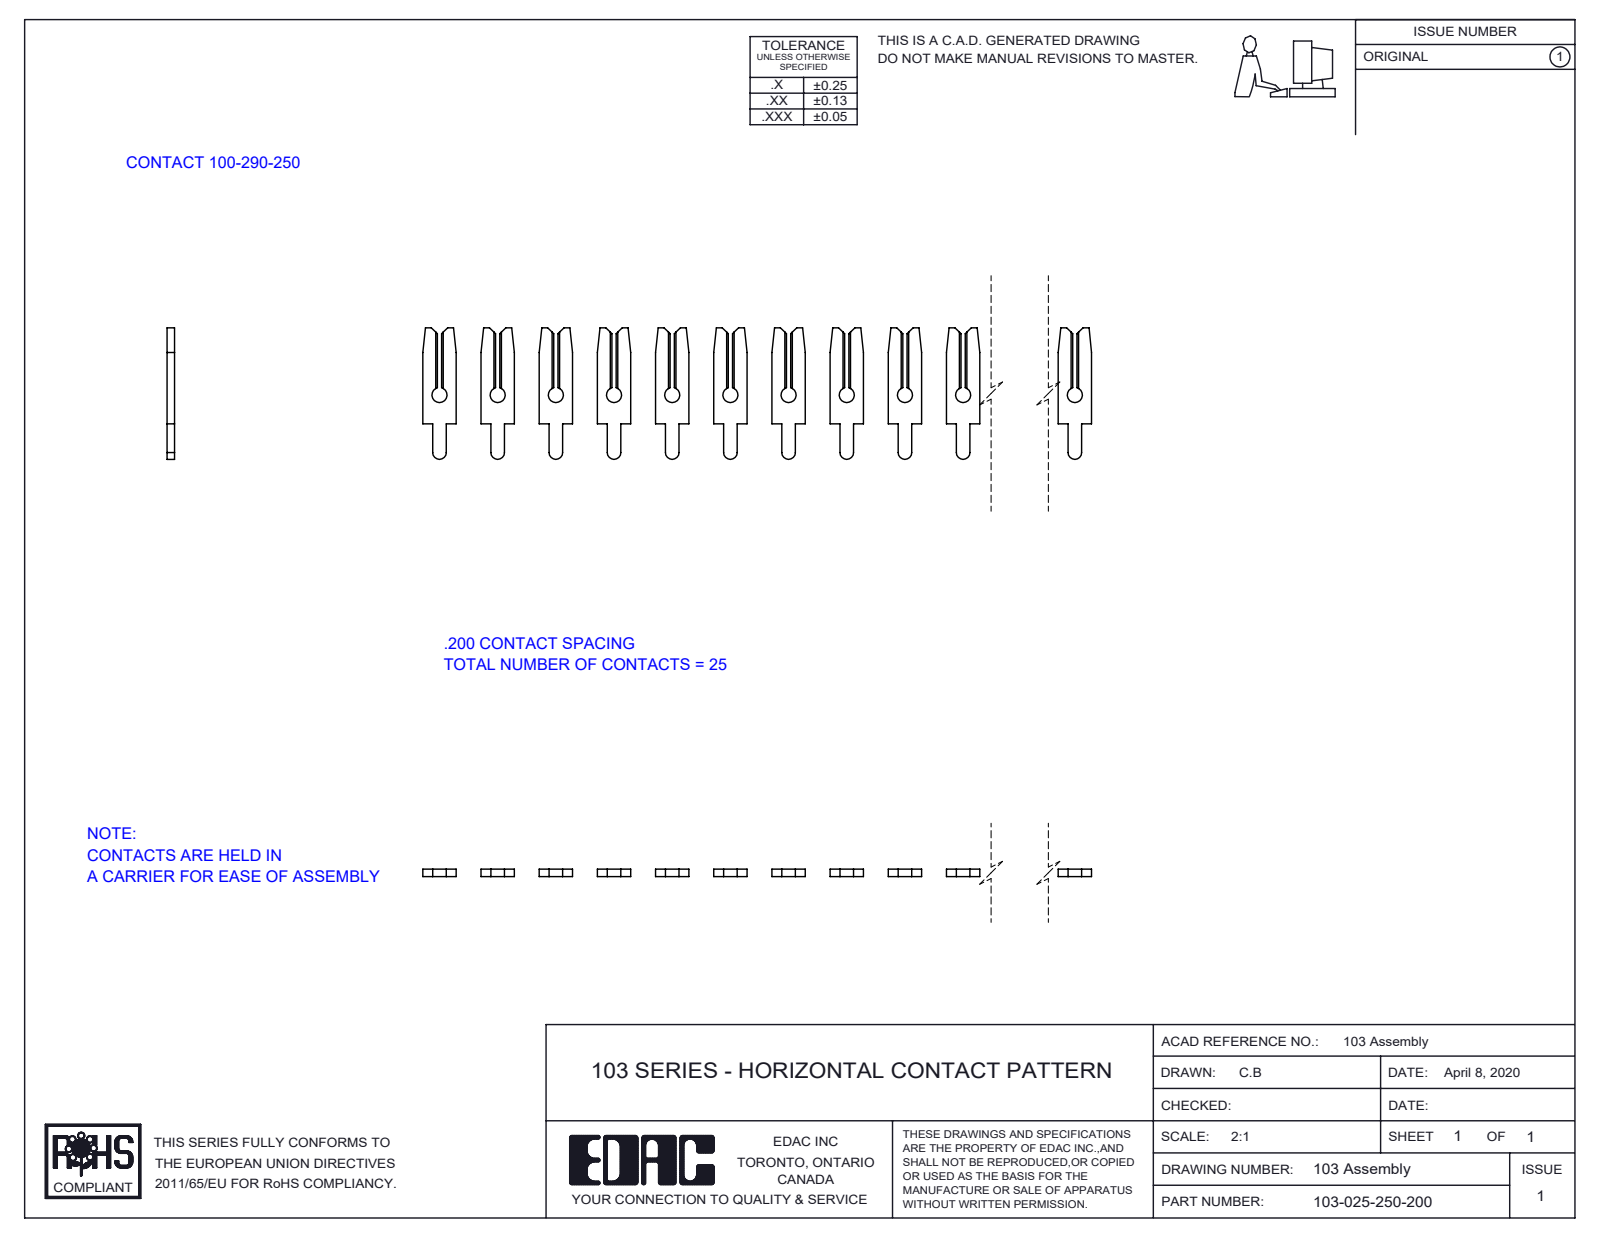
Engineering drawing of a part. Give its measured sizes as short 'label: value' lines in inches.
name: 103-025-250-200; 100-290-001_100-290-250
written by: SolidWorks 2016 (CONFIG_CONTROL_DESIGN)
unit: in
bodies: 25 solids, 600 faces (500 planar, 100 cylindrical, 0 other)
size: 4.915 × 0.452 × 0.026
volume: 0.024 in³; area: 2.842 in²
holes: 25× ⌀0.052
rounds: 25× R0.024
face distances: 0.026, 0.141, 0.2, 0.4, 0.283, 0.848, 0.6, 0.99, 0.707, 0.8
hole spacings: 0.2, 0.4, 0.6, 0.8, 1, 1.2, 1.4, 1.6
